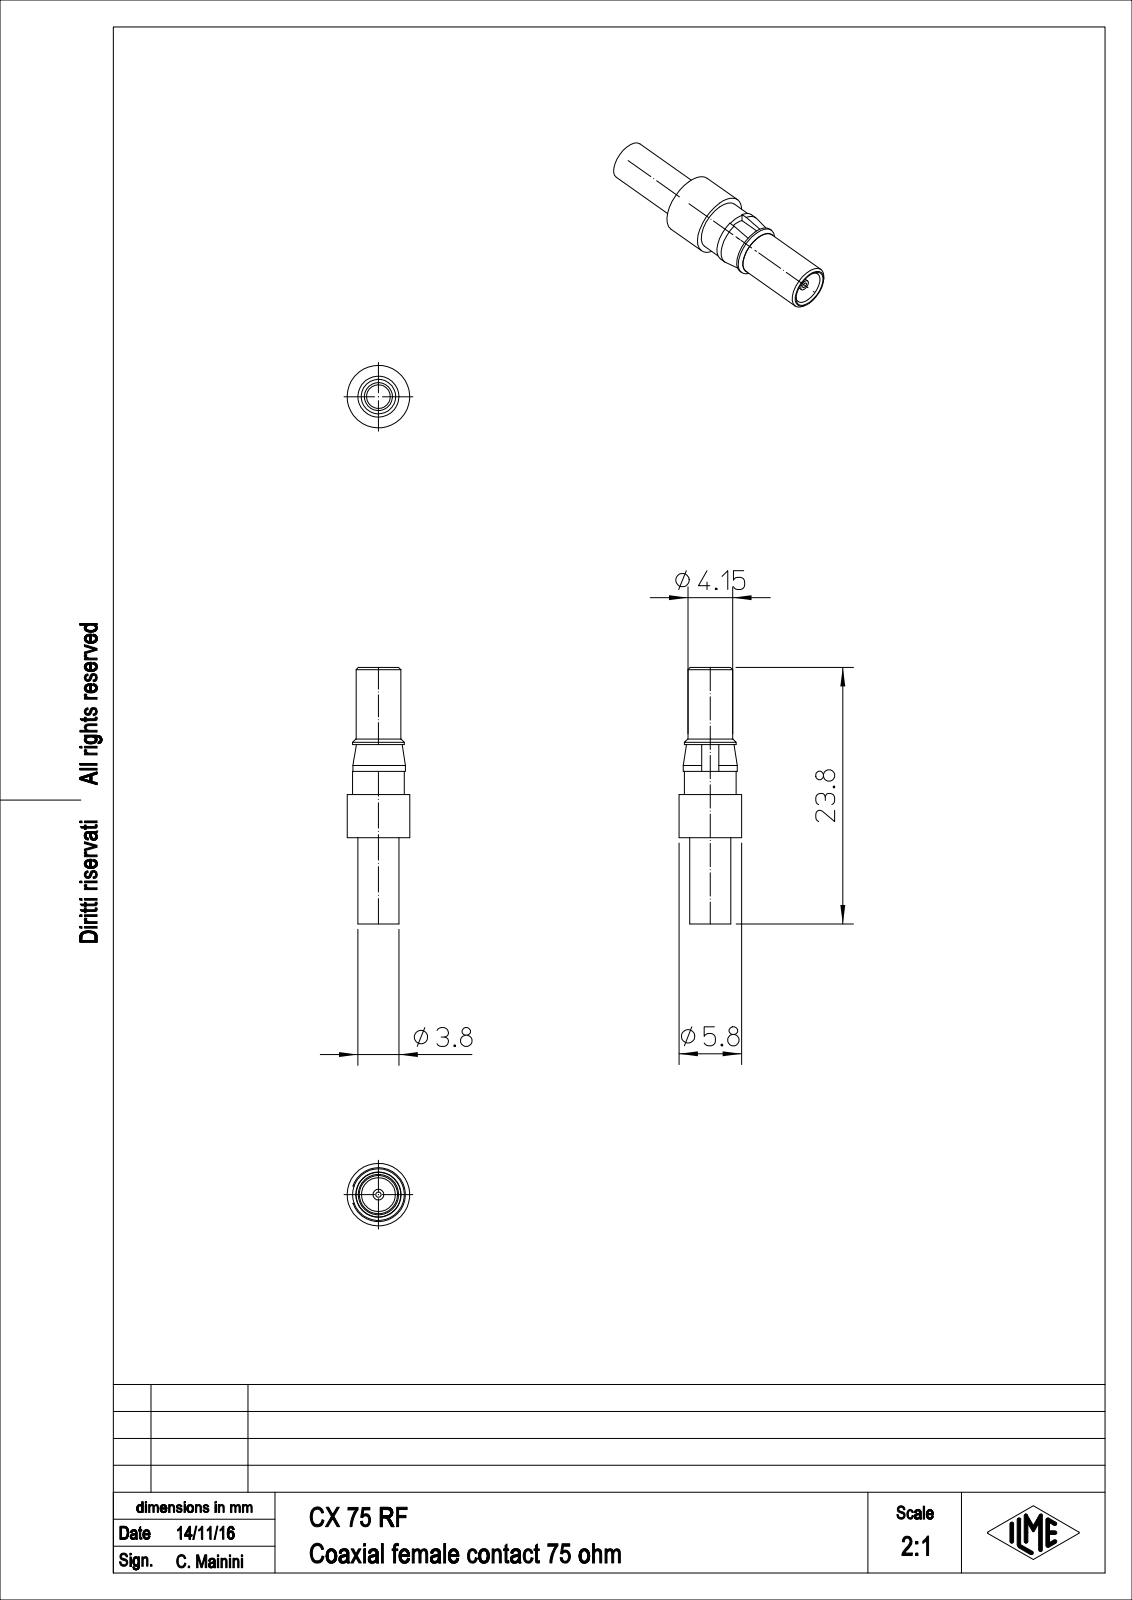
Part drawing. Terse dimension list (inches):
name: CX_75_RF
written by: PTC Creo Elements/Direct Modeling 19.0E 27-Jun-2016 (C) Parametric Technology GmbH (AUTOMOTIVE_DESIGN)
unit: in
bodies: 1 solid, 47 faces (16 planar, 24 cylindrical, 7 other)
size: 0.937 × 0.228 × 0.228
volume: 0.016 in³; area: 1.03 in²
holes: 1× ⌀0.02, 1× ⌀0.087, 1× ⌀0.124, 1× ⌀0.126
bosses: 1× ⌀0.228, 1× ⌀0.197, 1× ⌀0.189, 1× ⌀0.163, 1× ⌀0.15, 1× ⌀0.102, 1× ⌀0.039
rounds: 1× R0.069
face distances: 0.157, 0.215, 0.372, 0.031, 0.183, 0.341, 0.687, 0.656, 0.472, 0.315
